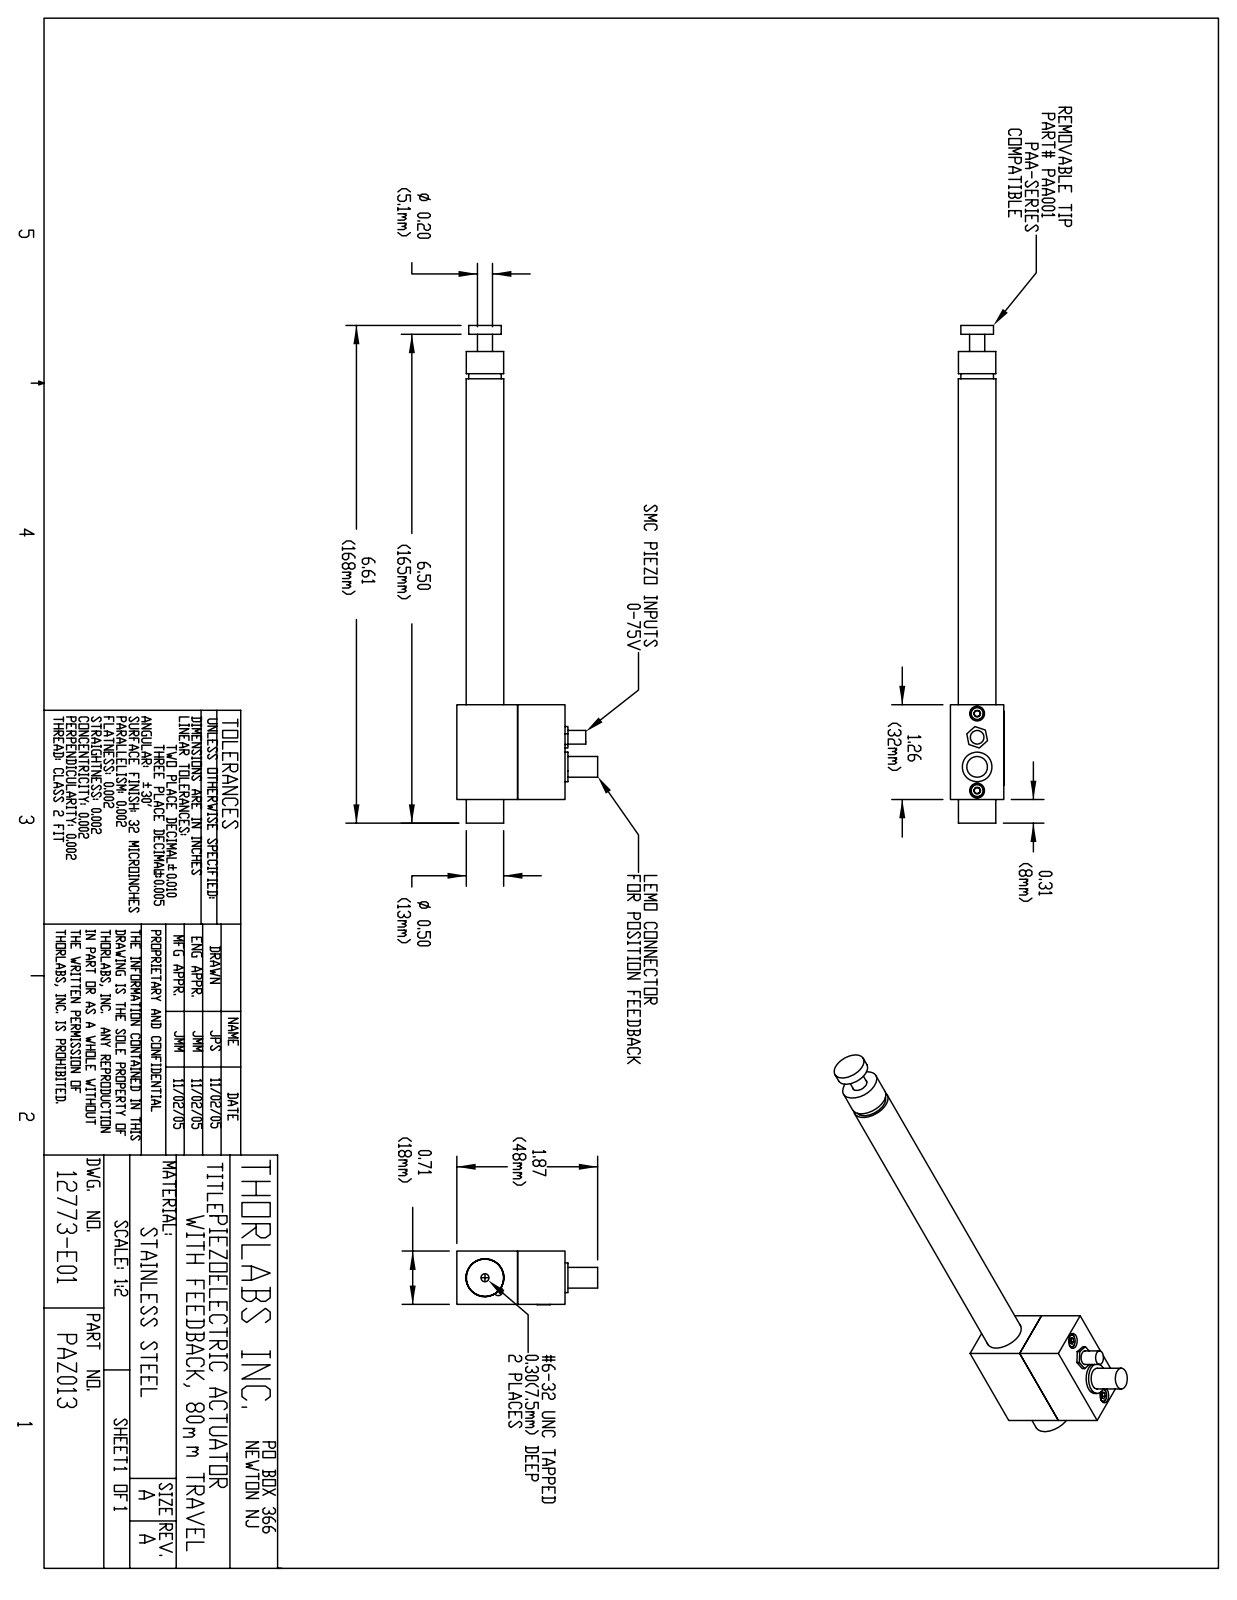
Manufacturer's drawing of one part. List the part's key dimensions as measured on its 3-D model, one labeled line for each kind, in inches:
Part name (STEP PRODUCT): 12773-E0W
STEP written by: SolidWorks 2007 (AUTOMOTIVE_DESIGN)
Units: inches
Bodies: 0 solids, 134 faces (83 planar, 38 cylindrical, 13 other)
Overall size (bounding box): 6.614 × 1.925 × 0.935
Round holes (diameter × count): ⌀0.098 ×2, ⌀0.197 ×2, ⌀0.107 ×1, ⌀0.209 ×1, ⌀0.504 ×1
Round bosses / shafts (diameter × count): ⌀0.5 ×1, ⌀0.496 ×1, ⌀0.433 ×1, ⌀0.394 ×1, ⌀0.276 ×1, ⌀0.201 ×1, ⌀0.181 ×1
Partial cylindrical surfaces — rounded edges, fillets, slot ends (radius × count): R0.087 ×2, R0.059 ×1
Main face-to-face distances: 0.708, 1.26, 1.436, 0.63, 0.807, 1.575, 0.315, 4.693, 5.953, 6.268
Hole centre spacings: 1.024
